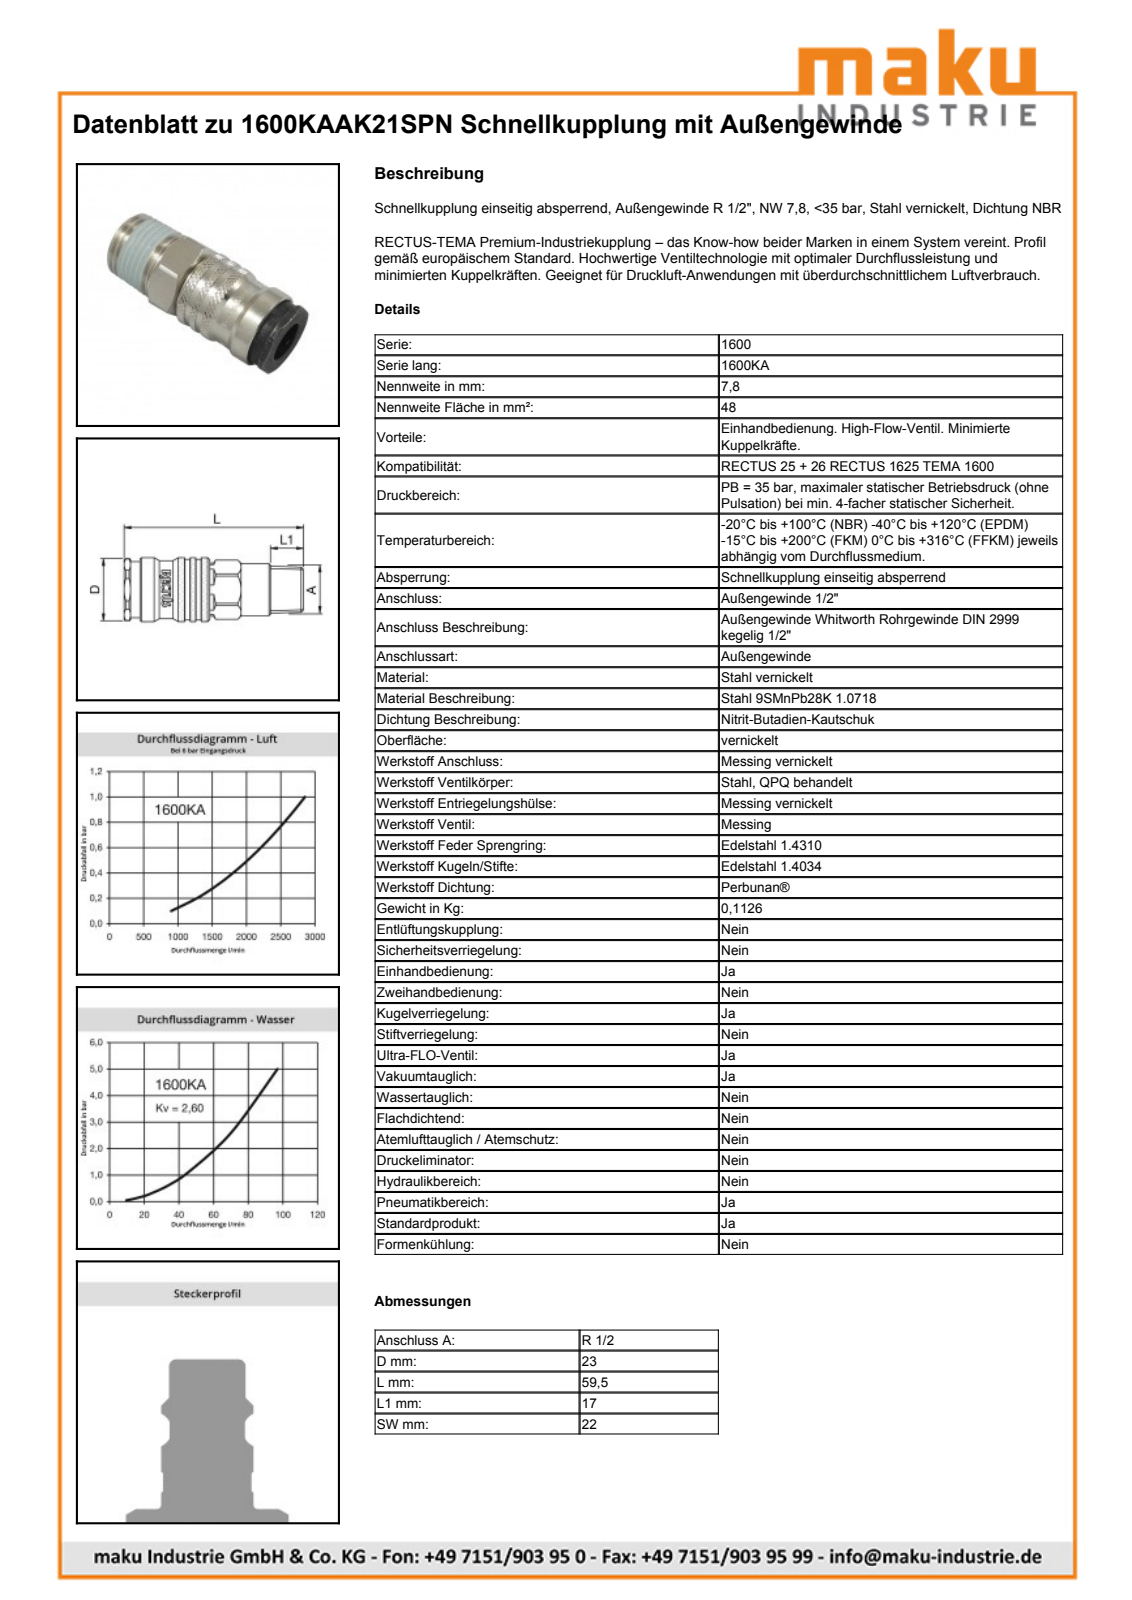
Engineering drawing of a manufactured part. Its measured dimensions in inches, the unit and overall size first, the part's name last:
Units: inches
Overall size (bounding box): 2.326 × 0.961 × 0.944
Round holes (diameter × count): ⌀0.636 ×1, ⌀0.677 ×1, ⌀0.705 ×1, ⌀0.772 ×1, ⌀0.815 ×1
Round bosses / shafts (diameter × count): ⌀0.911 ×1, ⌀0.866 ×1, ⌀0.827 ×1, ⌀0.799 ×1, ⌀0.76 ×1, ⌀0.693 ×1, ⌀0.669 ×1, ⌀0.618 ×1
Partial cylindrical surfaces — rounded edges, fillets, slot ends (radius × count): R0.298 ×1, R0.409 ×1, R0.443 ×1, R0.488 ×1
Main face-to-face distances: 2.326, 0.866, 0.865, 1.047, 1.28, 1.222, 1.104, 0.175, 0.827, 0.996
Volume: 1.271 in³ · Surface area: 14.14 in²
Bodies: 2 solids, 616 faces (208 planar, 85 cylindrical, 323 other)
Part name (STEP PRODUCT): D106871
STEP written by: Autodesk Inventor 2013 (AUTOMOTIVE_DESIGN)
